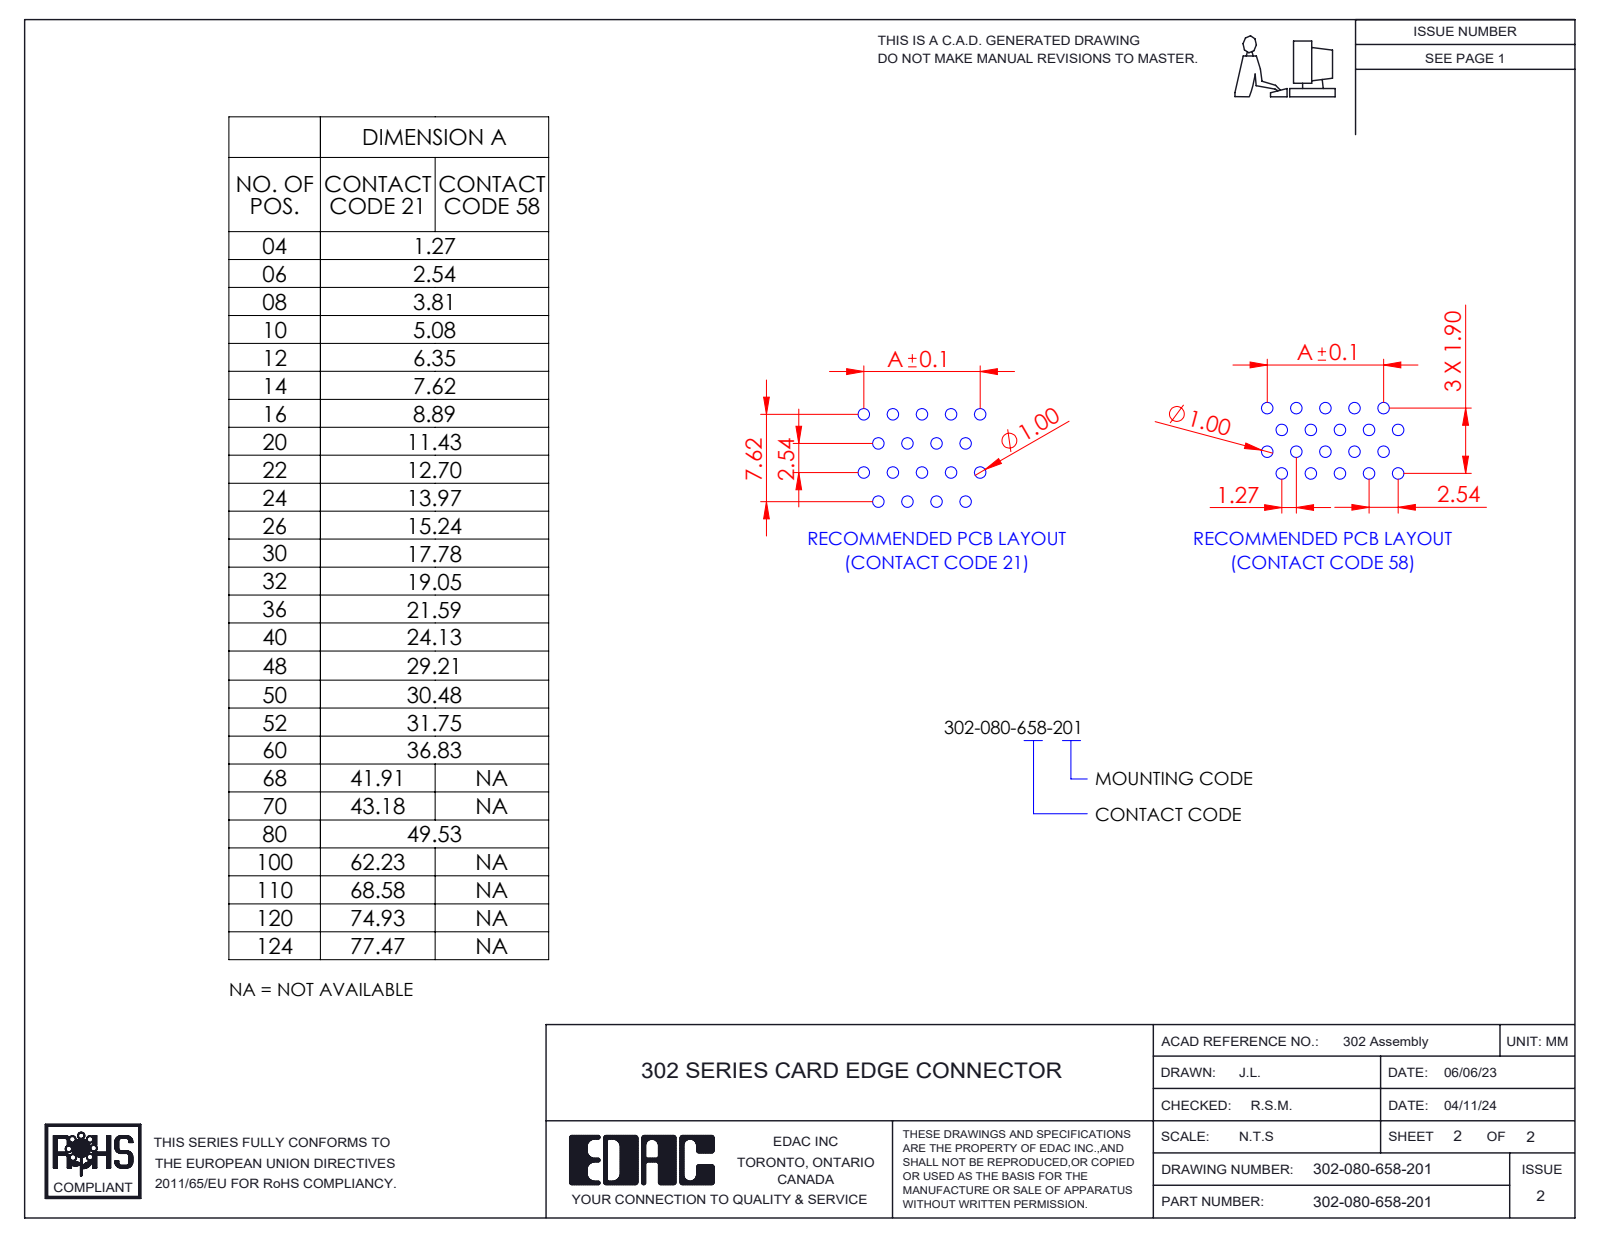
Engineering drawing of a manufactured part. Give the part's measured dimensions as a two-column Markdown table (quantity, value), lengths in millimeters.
| quantity | value |
| --- | --- |
| part name | Contact_302-290-X58-003; Contact_302-290-X58-002; HSG_RA HSG (80P); Contact_302-290-X58-001 (+2 more) |
| STEP written by | SolidWorks 2023 (CONFIG_CONTROL_DESIGN) |
| units | millimeters |
| bodies | 81 solids, 4227 faces (3007 planar, 1056 cylindrical, 164 other) |
| overall size | 56.9 × 21.37 × 11.68 |
| volume | 5 033 mm³ |
| surface area | 14 435 mm² |
| partial cylindrical surfaces (radius × count) | 0.2 × 88, 0.25 × 80, 0.5 × 4, 2.03 × 3, 0.11 × 2, 0.4 × 2, 0.41 × 2, 0.8 × 2 |
| main face-to-face distances | 1.27, 2.54, 3.81, 5.08, 1.9, 7.62, 6.35, 8.88, 8.89, 10.16 |
